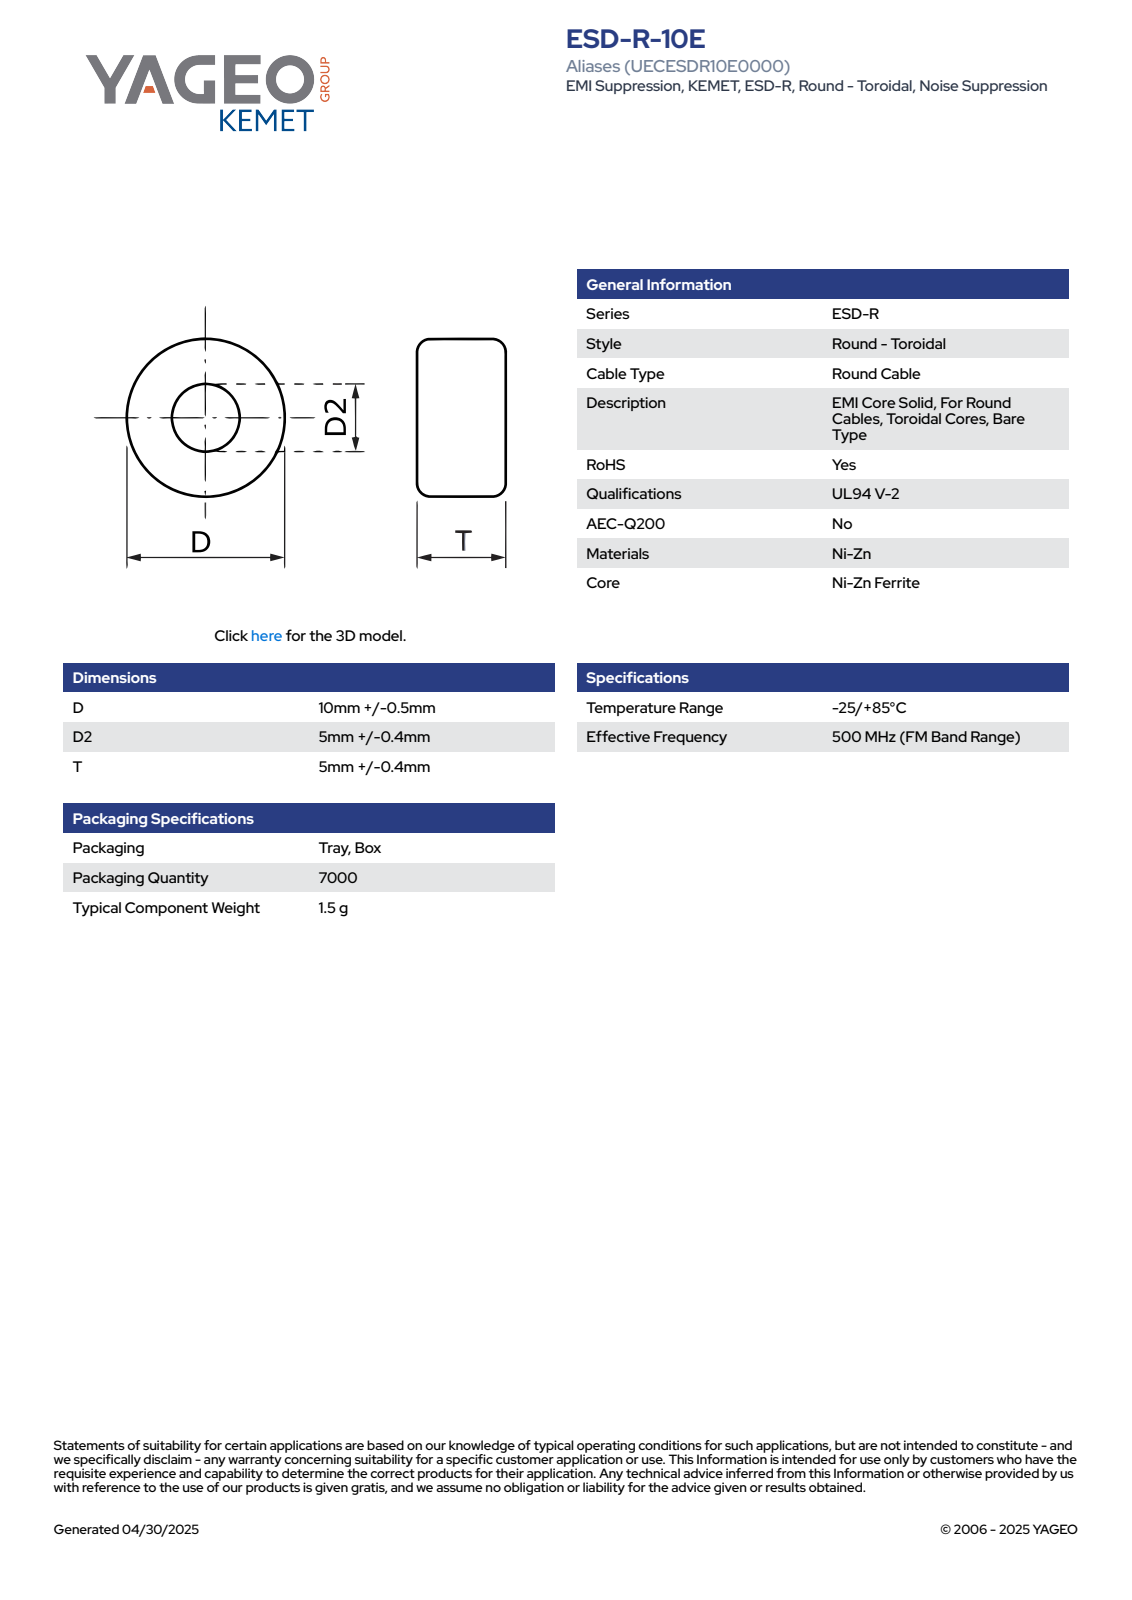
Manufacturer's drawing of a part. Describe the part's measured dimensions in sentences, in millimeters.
The part is named "EC_KBC_D10.5D25T5.4". Its 3-D file was written by "SolidWorks 2021 (AUTOMOTIVE_DESIGN)". It is 1 solid with 66 faces: 24 planar, 7 cylindrical and 35 other. Overall it measures 10.51 by 10.5 by 5.4 millimeters. Its volume is 360 cubic millimeters and its surface area 389 square millimeters. Round holes: 1 of diameter 5. Round bosses or shafts: 1 of diameter 10.5. Partial cylindrical surfaces (rounded edges, fillets, slot ends): 1 of radius 5.26. The main face-to-face distances are 5.4, 1.85, 3.55, 1.7, 0.32, 2.17, 3.23, 1.38, 1.06, 2.91.
